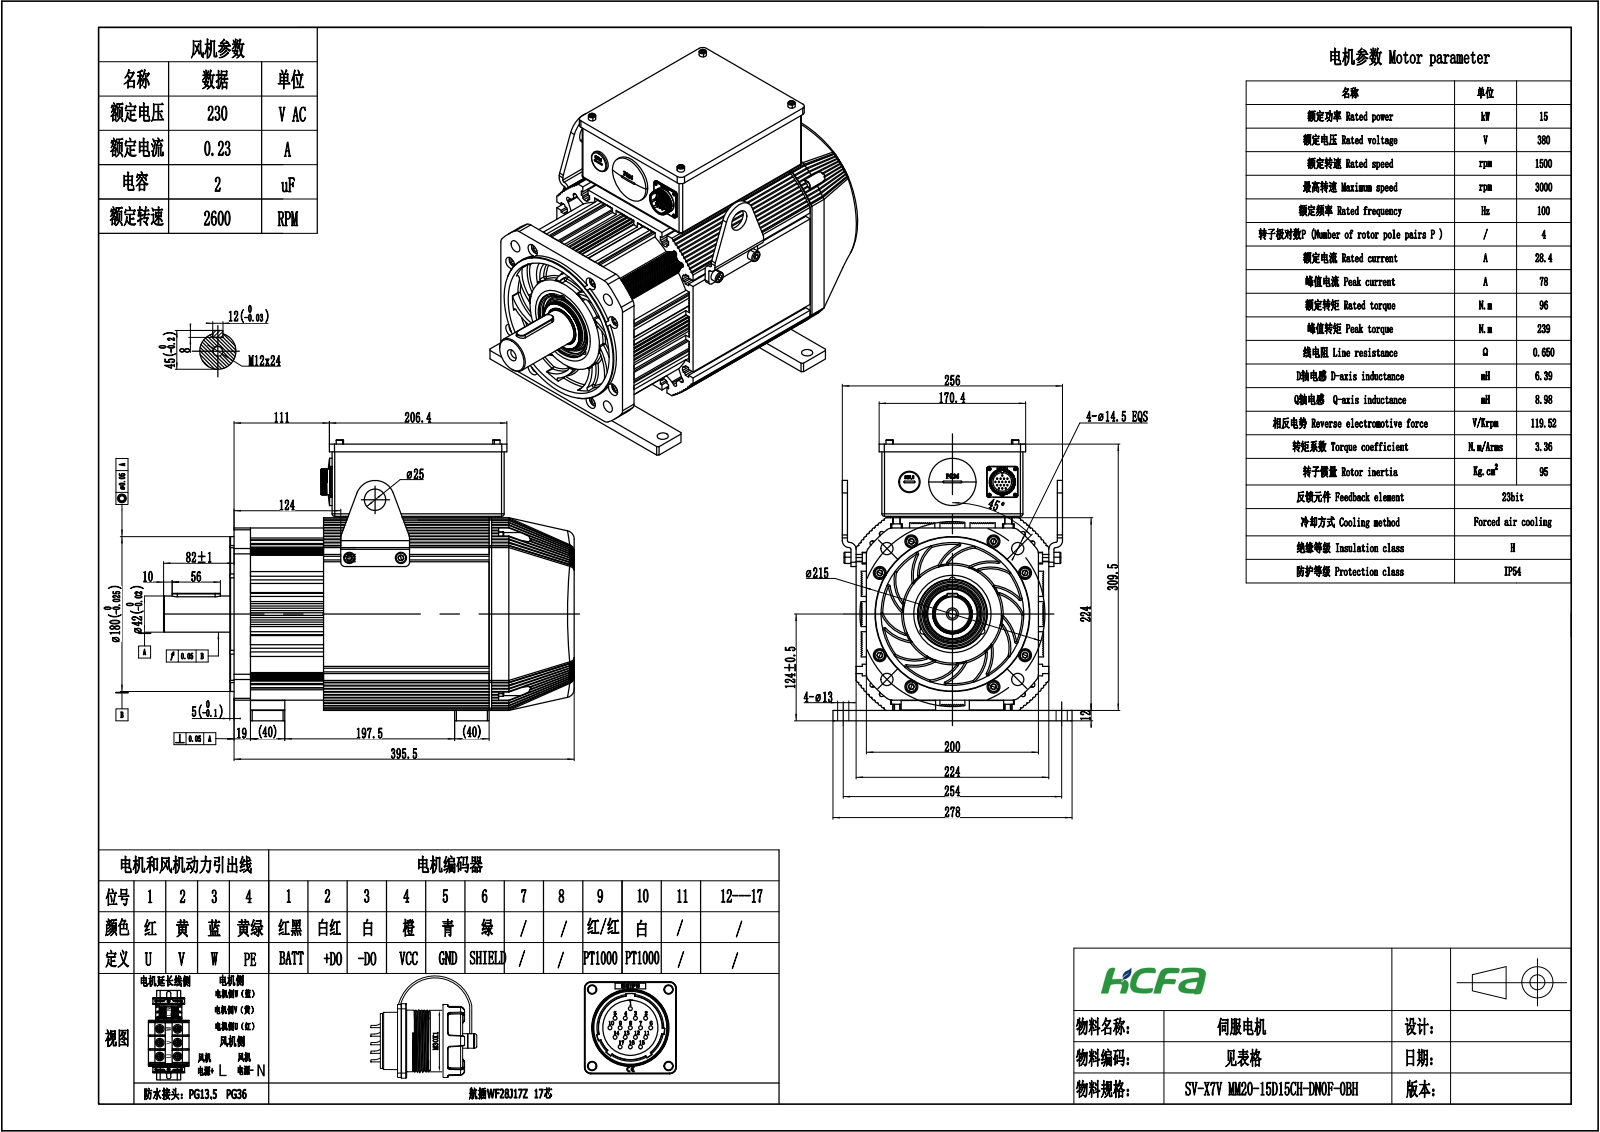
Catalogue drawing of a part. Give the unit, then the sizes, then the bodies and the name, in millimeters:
Units: millimetres
Overall size (bounding box): 477.5 × 326.5 × 278
Round holes (diameter × count): ⌀9 ×22, ⌀15 ×14, ⌀5 ×9, ⌀13 ×8, ⌀2.5 ×4, ⌀6.8 ×4, ⌀7 ×4, ⌀10 ×4, ⌀14.5 ×4, ⌀10.2 ×1, ⌀20.5 ×1, ⌀21.7 ×1
Round bosses / shafts (diameter × count): ⌀8 ×20, ⌀1.5 ×17, ⌀13 ×16, ⌀8.5 ×4, ⌀10 ×3, ⌀6 ×3, ⌀40 ×2, ⌀183 ×1
Partial cylindrical surfaces — rounded edges, fillets, slot ends (radius × count): R2 ×112, R1 ×20, R1.5 ×20, R5 ×18, R1.4 ×16, R3 ×12, R0.2 ×10, R10 ×10
Main face-to-face distances: 2, 224, 12, 6, 307.5, 309.5, 212, 30, 194, 32
Hole centre spacings: 29.47, 43.17, 97, 124.07, 137.18, 138.41, 162.9, 167.15
Volume: 16 500 000 mm³ · Surface area: 1 051 000 mm²
Bodies: 11 solids, 3575 faces (1428 planar, 1191 cylindrical, 956 other)
Part name (STEP PRODUCT): 10002030101-0032-SV-X7VMM20-15D15CH-DN0F-0BH-4段外形图
STEP written by: SolidWorks 2021 (CONFIG_CONTROL_DESIGN)
